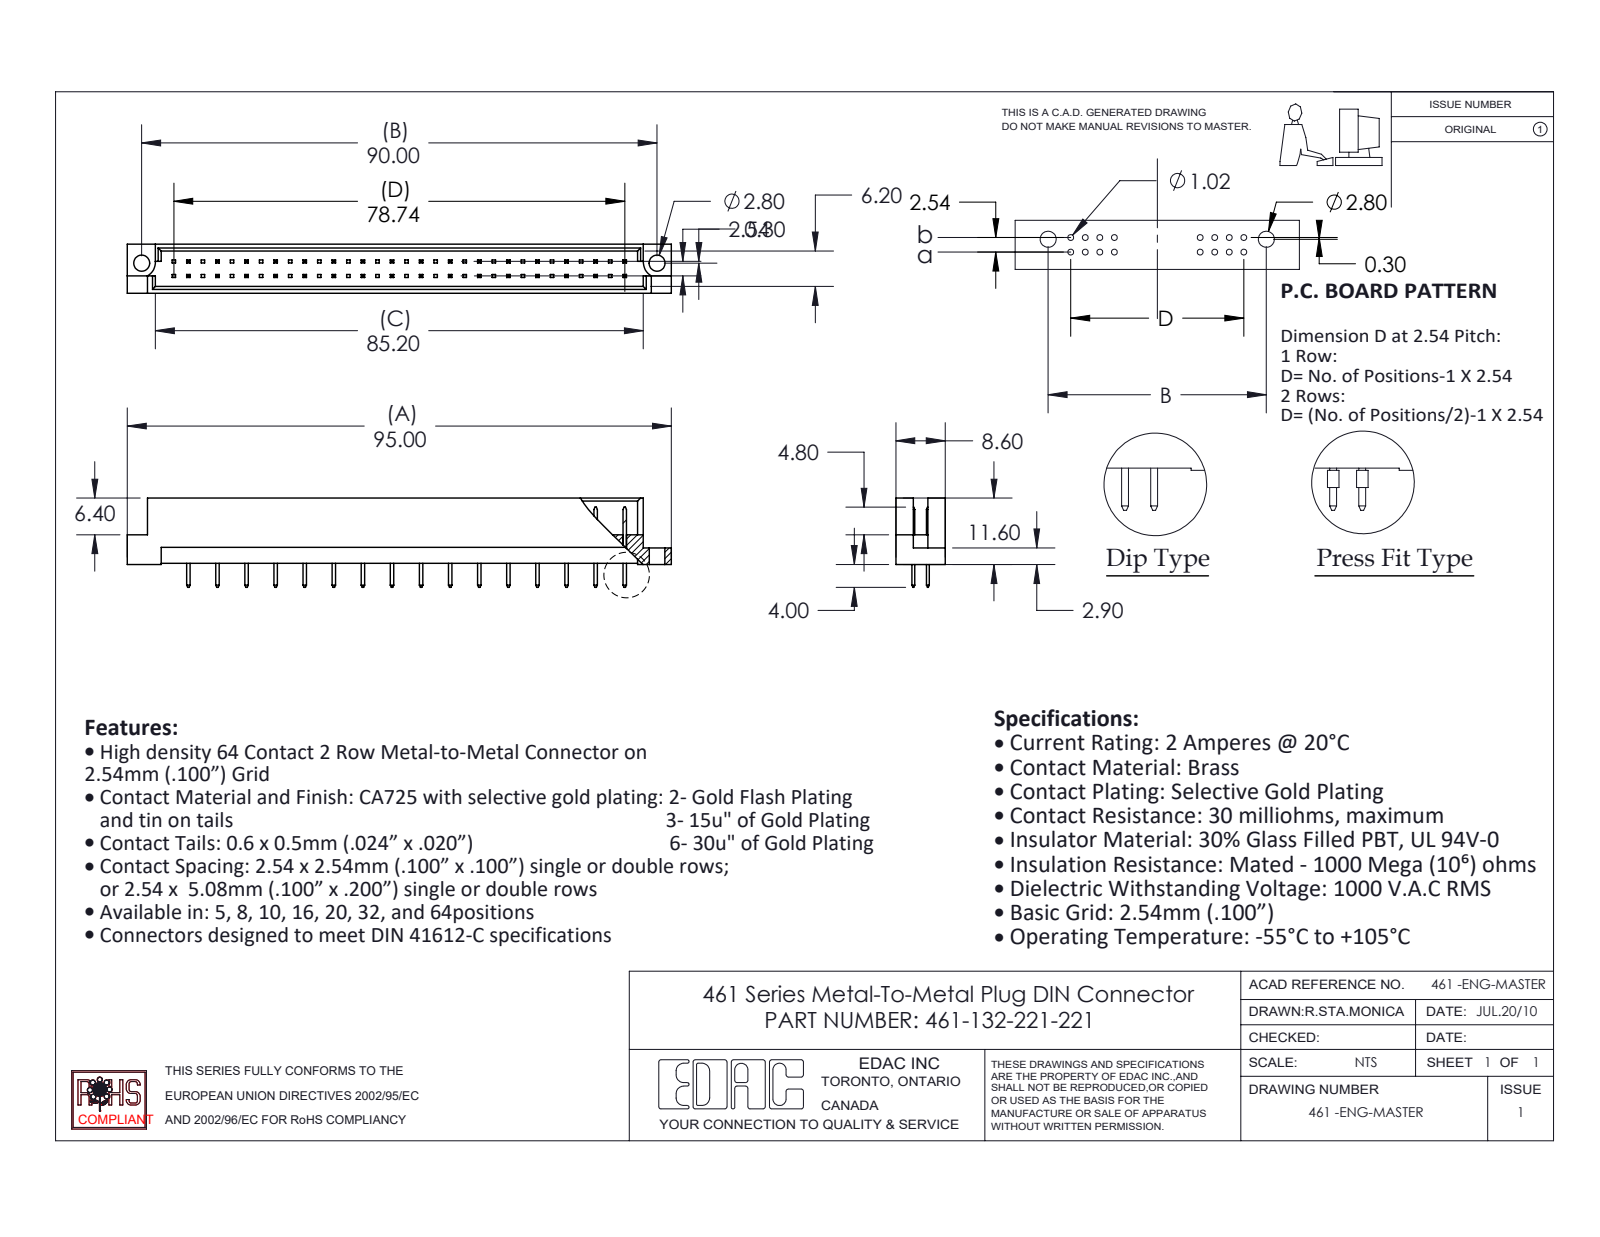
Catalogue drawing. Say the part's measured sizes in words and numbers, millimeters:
The part is named "461-290_21; 461 Part_64; 461-132-221-221". Its 3-D file was written by "SolidWorks 2020 (CONFIG_CONTROL_DESIGN)". It is 33 solids with 753 faces: 746 planar, 7 cylindrical and 0 other. Overall it measures 95 by 15.6 by 8.6 millimeters. Its volume is 4 787 cubic millimeters and its surface area 6 645 square millimeters. Round holes: 2 of diameter 2.8. Partial cylindrical surfaces (rounded edges, fillets, slot ends): 2 of radius 2.8. The main face-to-face distances are 1.2, 7.4, 8.6, 6.2, 5, 2.54, 3.28, 5.32, 2.08, 4.12. The hole center spacings are 90.
